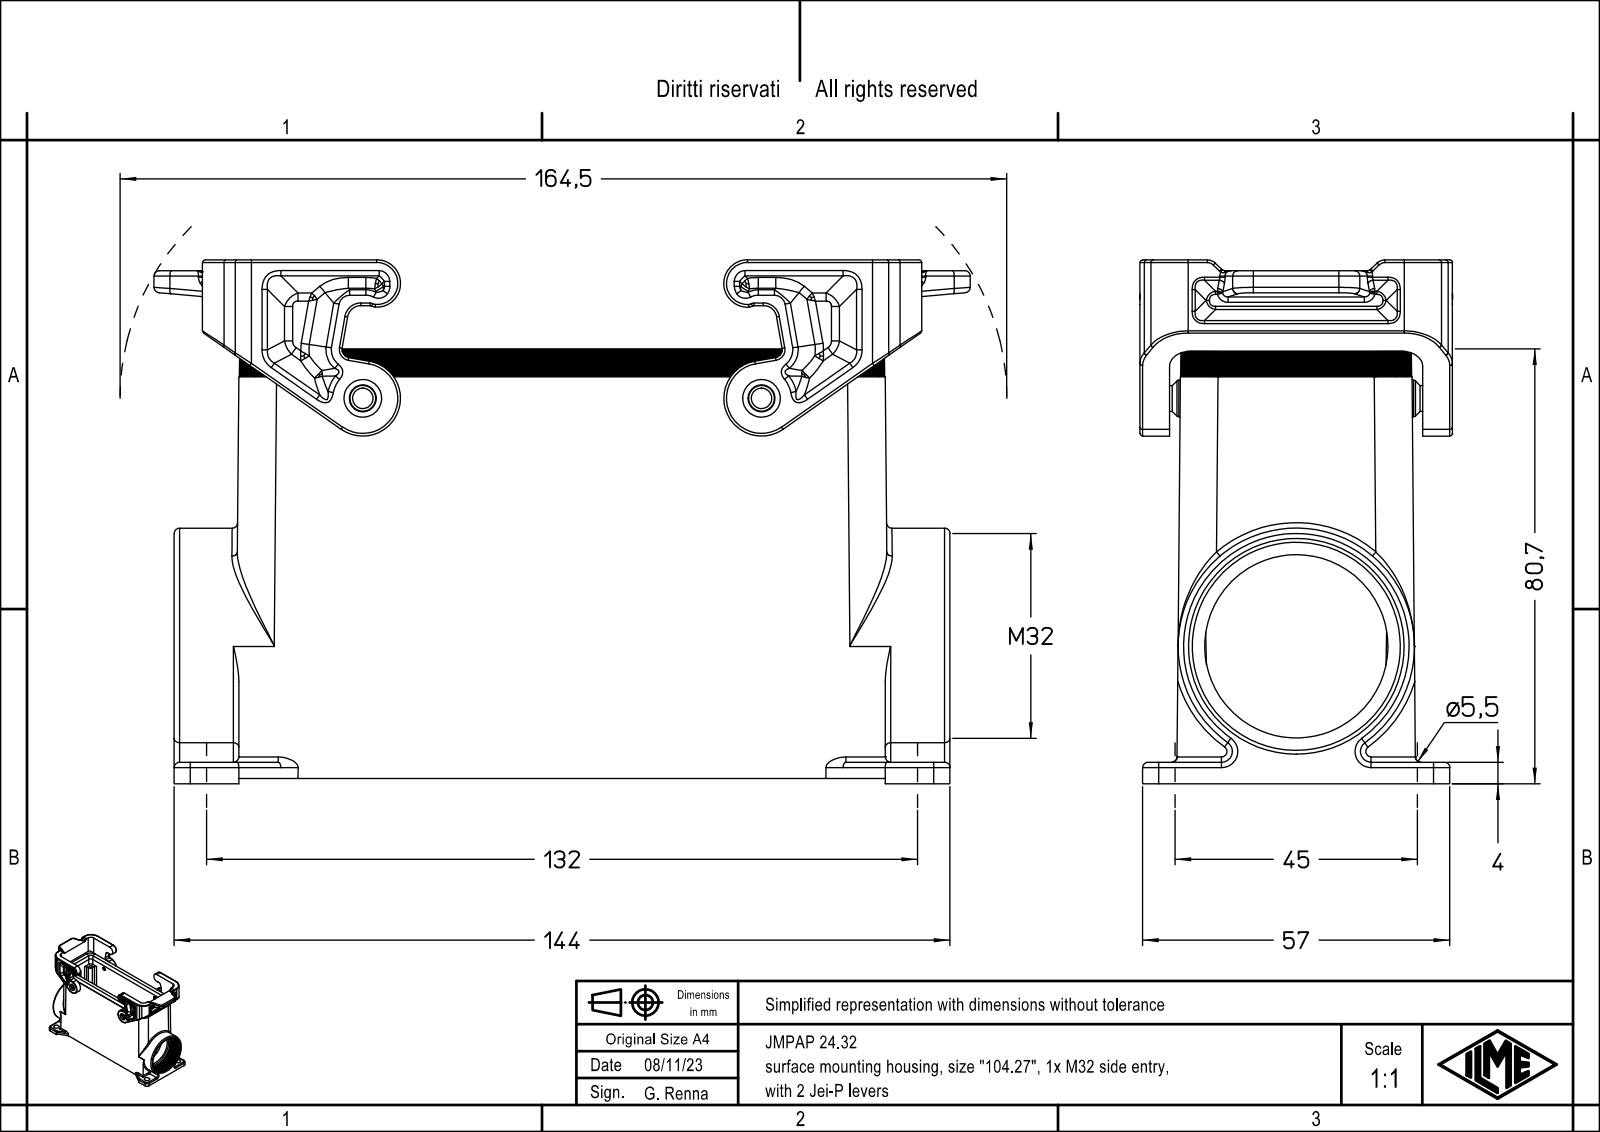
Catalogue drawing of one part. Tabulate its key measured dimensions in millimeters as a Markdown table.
| quantity | value |
| --- | --- |
| part name | JMPAP 24.32 |
| STEP written by | Creo Elements/Direct Modeling 20.1B 02-Apr-2019 (C) Parametric Technology GmbH (AUTOMOTIVE_DESIGN) |
| units | millimeters |
| bodies | 1 solid, 867 faces (173 planar, 314 cylindrical, 380 other) |
| overall size | 151.5 × 97.2 × 58.08 |
| volume | 181 447 mm³ |
| surface area | 78 569 mm² |
| round holes (diameter × count) | 3 × 4, 3.5 × 4, 5.5 × 4, 4.8 × 2, 28 × 1, 30.6 × 1 |
| round bosses / shafts (diameter × count) | 6.8 × 2, 43.87 × 1 |
| partial cylindrical surfaces (radius × count) | 0.5 × 50, 1 × 44, 3 × 38, 2 × 26, 1.5 × 12, 4 × 12, 6 × 12, 7 × 10 |
| main face-to-face distances | 3, 1, 4, 47, 10.25, 133.75, 38.9, 7, 5.5, 52.5 |
| hole center spacings | 16.64, 38.63, 118.34, 123.37, 27, 45, 104, 107.45 |
